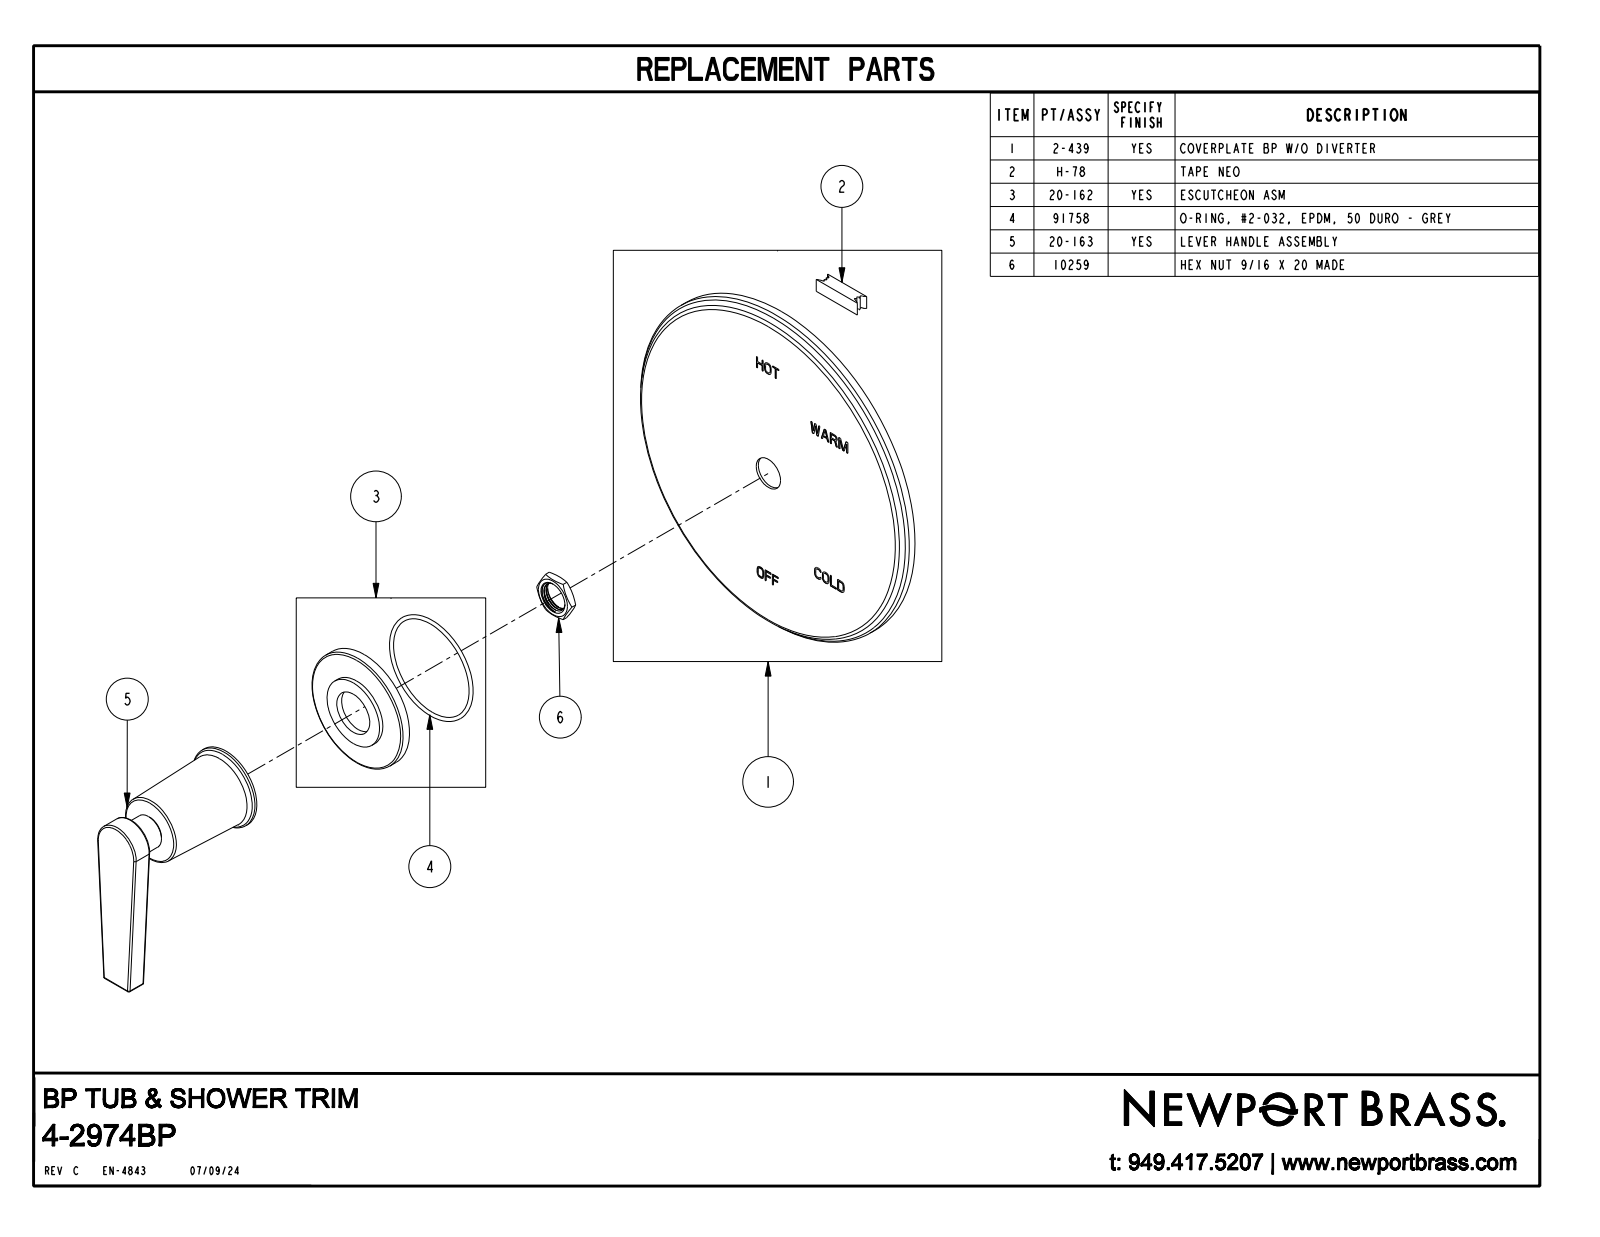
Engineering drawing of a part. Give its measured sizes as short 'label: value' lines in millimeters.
name: 4-2974BP
written by: CREO PARAMETRIC BY PTC INC, 2018400 (CONFIG_CONTROL_DESIGN)
unit: mm
bodies: 1 solid, 389 faces (340 planar, 25 cylindrical, 24 other)
size: 165.1 × 165.1 × 80.8
volume: 235 600 mm³; area: 57 280 mm²
holes: 1× ⌀11.8
bosses: 1× ⌀165.1, 1× ⌀55.9, 1× ⌀38.1, 1× ⌀32.4, 1× ⌀15.9, 1× ⌀13.3, 1× ⌀10.9
rounds: 8× R0.8, 1× R11.7
face distances: 8, 4.7, 12.7, 80.8, 72.9, 68.1, 71.3, 63.4, 58.6, 9.5
